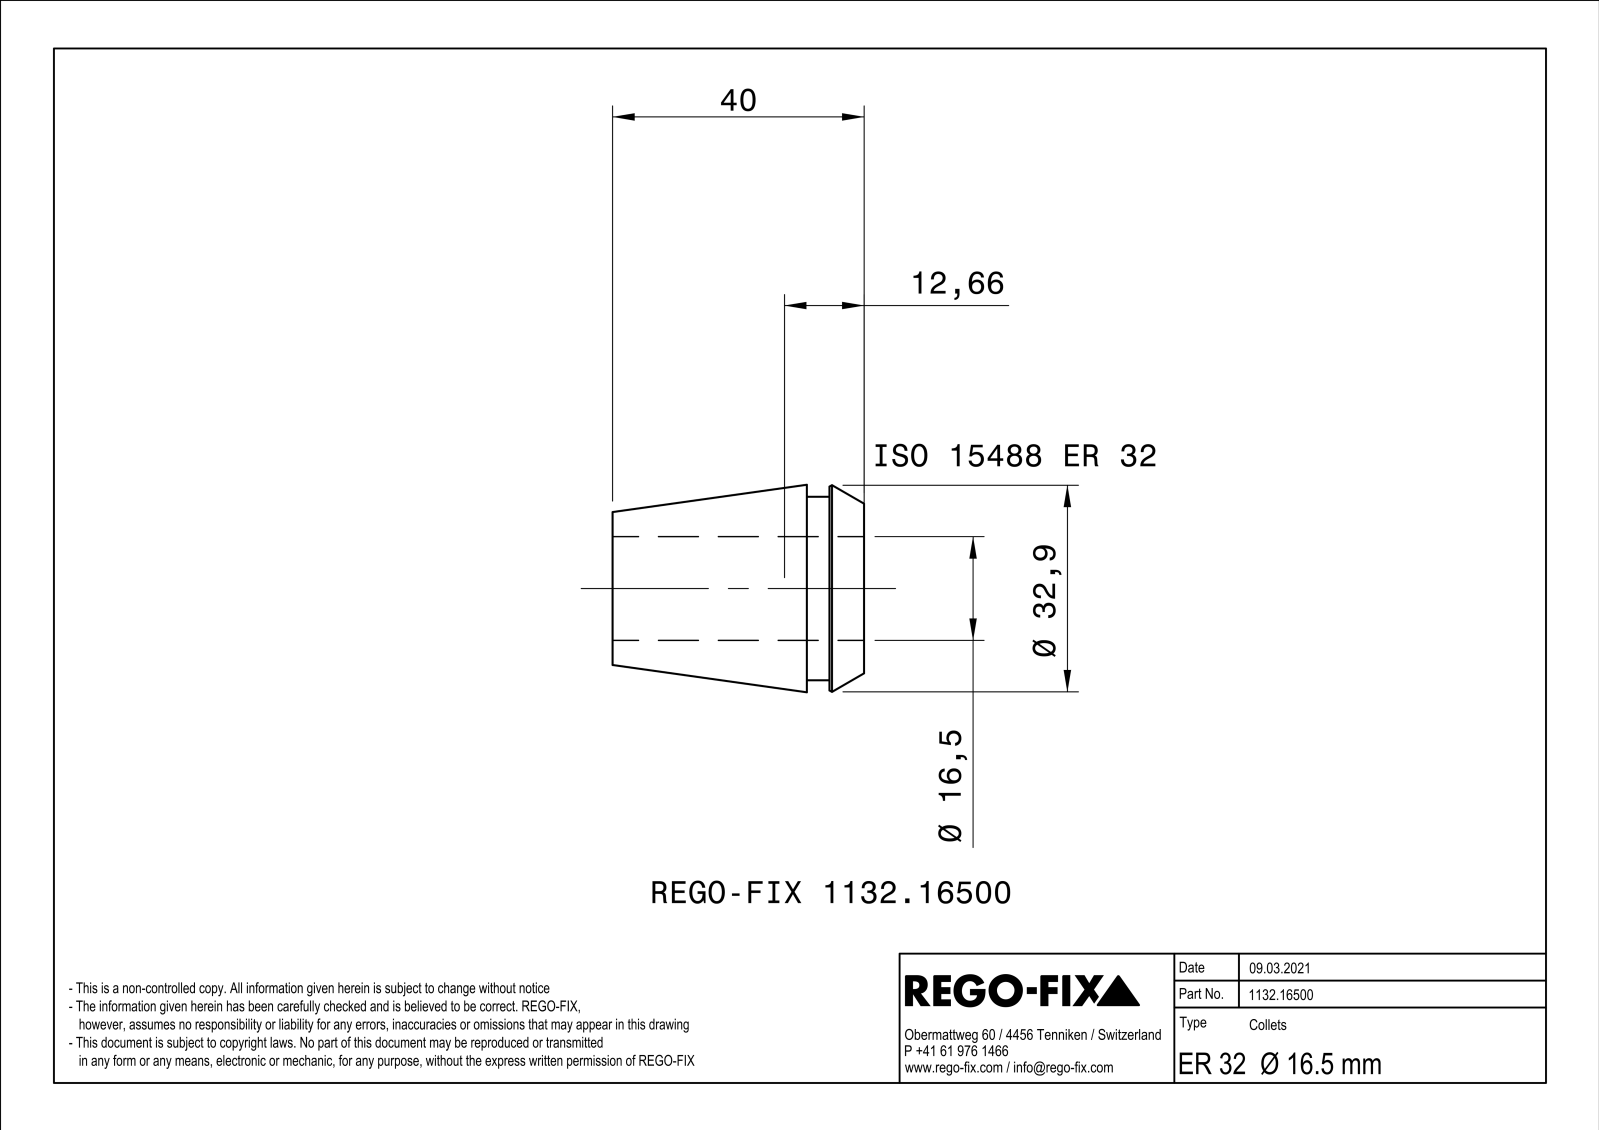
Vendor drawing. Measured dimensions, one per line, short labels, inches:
name: NOCUT
written by: SIEMENS PLM Software Solid Edge ST10 (AUTOMOTIVE_DESIGN)
unit: in
bodies: 1 solid, 209 faces (88 planar, 41 cylindrical, 80 other)
size: 1.575 × 1.298 × 1.298
volume: 0.875 in³; area: 19.58 in²
holes: 1× ⌀0.65
bosses: 1× ⌀1.15
rounds: 20× R0.016
face distances: 0.039, 1.575, 0.358, 1.217, 0.217, 0.142, 1.358, 0.236, 0.02, 0.122
